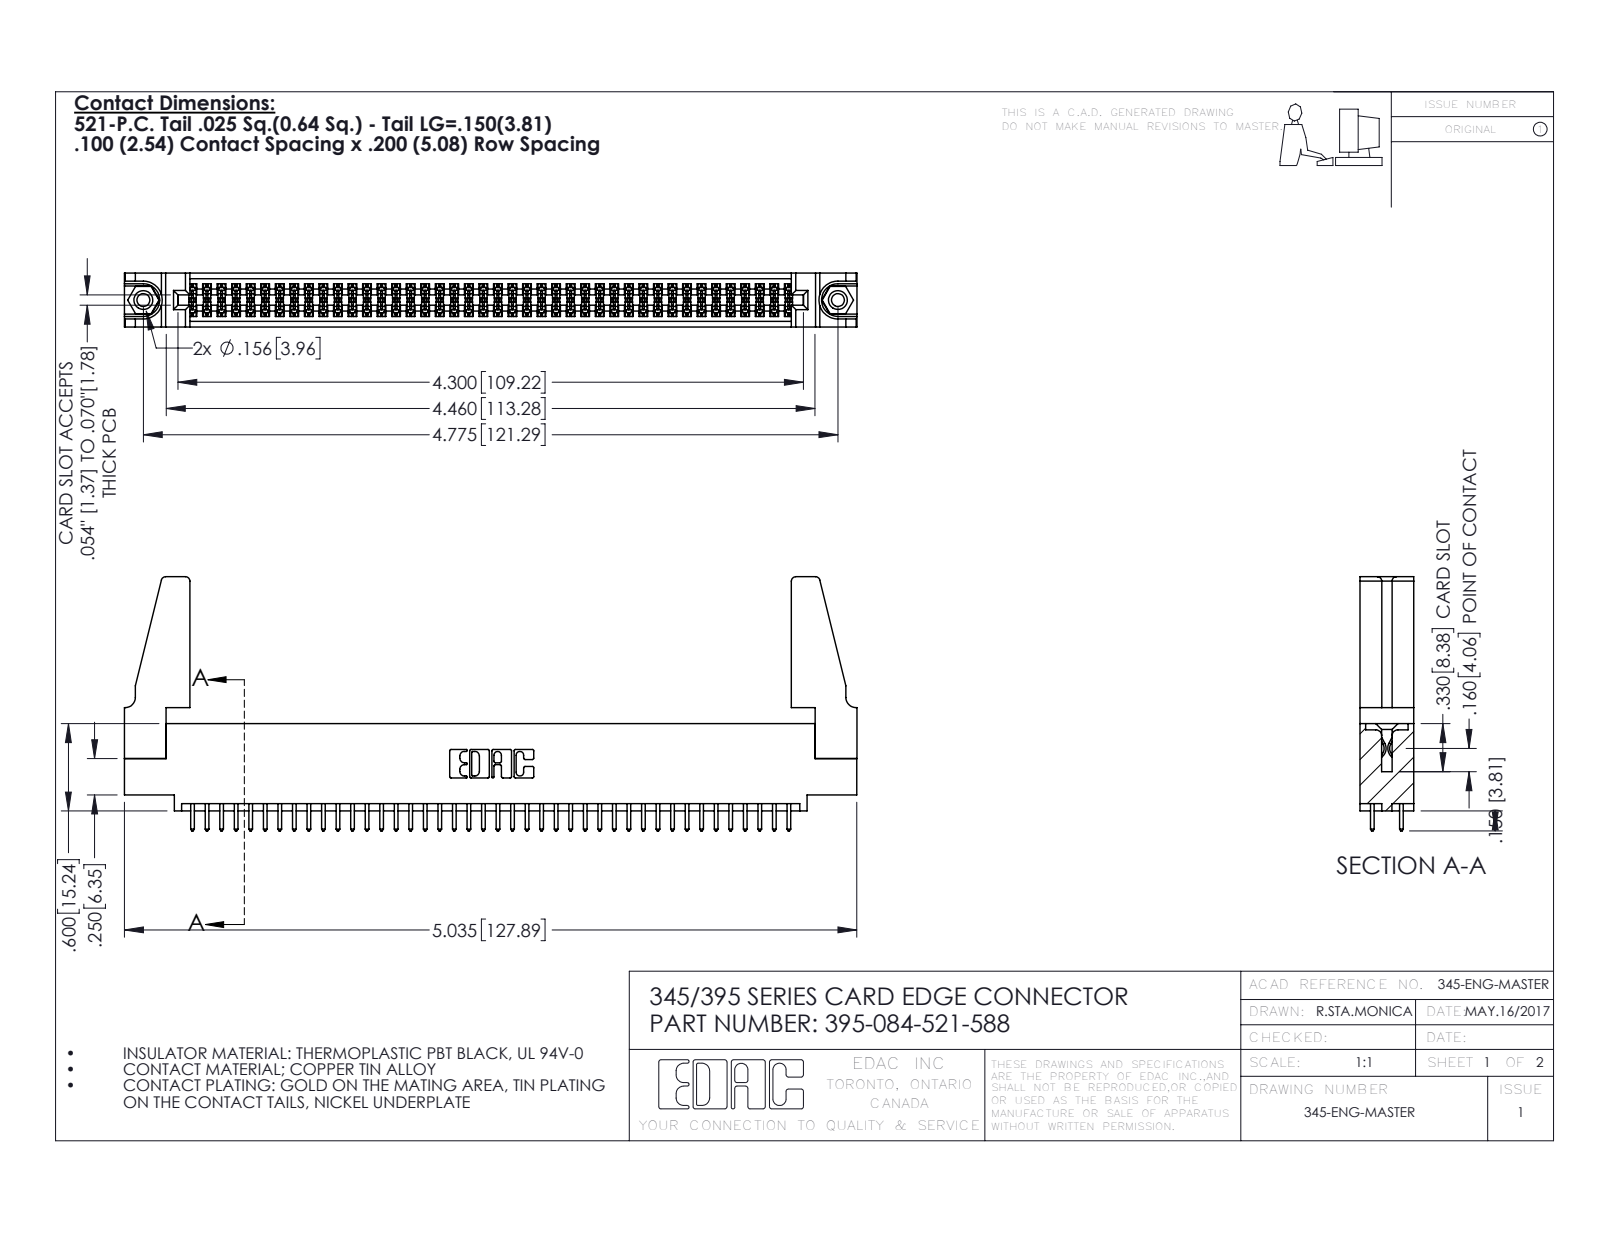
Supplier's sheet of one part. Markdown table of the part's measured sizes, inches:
| quantity | value |
| --- | --- |
| part name | 345-250-001_345-250-001-102; 345 Part_0.110 Offset - 0.156 Dia-TH; 345-220-078_345-220-088; 395-084-521-588 (+1 more) |
| STEP written by | SolidWorks 2016 (CONFIG_CONTROL_DESIGN) |
| units | inches |
| bodies | 89 solids, 4454 faces (2928 planar, 1510 cylindrical, 16 other) |
| overall size | 5.036 × 1.747 × 0.37 |
| volume | 0.95 in³ |
| surface area | 32.86 in² |
| round holes (diameter × count) | 0.089 × 2, 0.125 × 2, 0.156 × 2, 0.064 × 1 |
| round bosses / shafts (diameter × count) | 0.155 × 2 |
| partial cylindrical surfaces (radius × count) | 0.006 × 126, 0.01 × 84, 0.01 × 22, 0.03 × 8, 0.007 × 6, 0.031 × 6, 0.026 × 3, 0.014 × 2 |
| main face-to-face distances | 0.072, 0.298, 0.37, 0.2, 0.098, 0.272, 0.025, 0.225, 0.175, 0.149 |
| hole center spacings | 0.27, 4.539, 4.775 |
